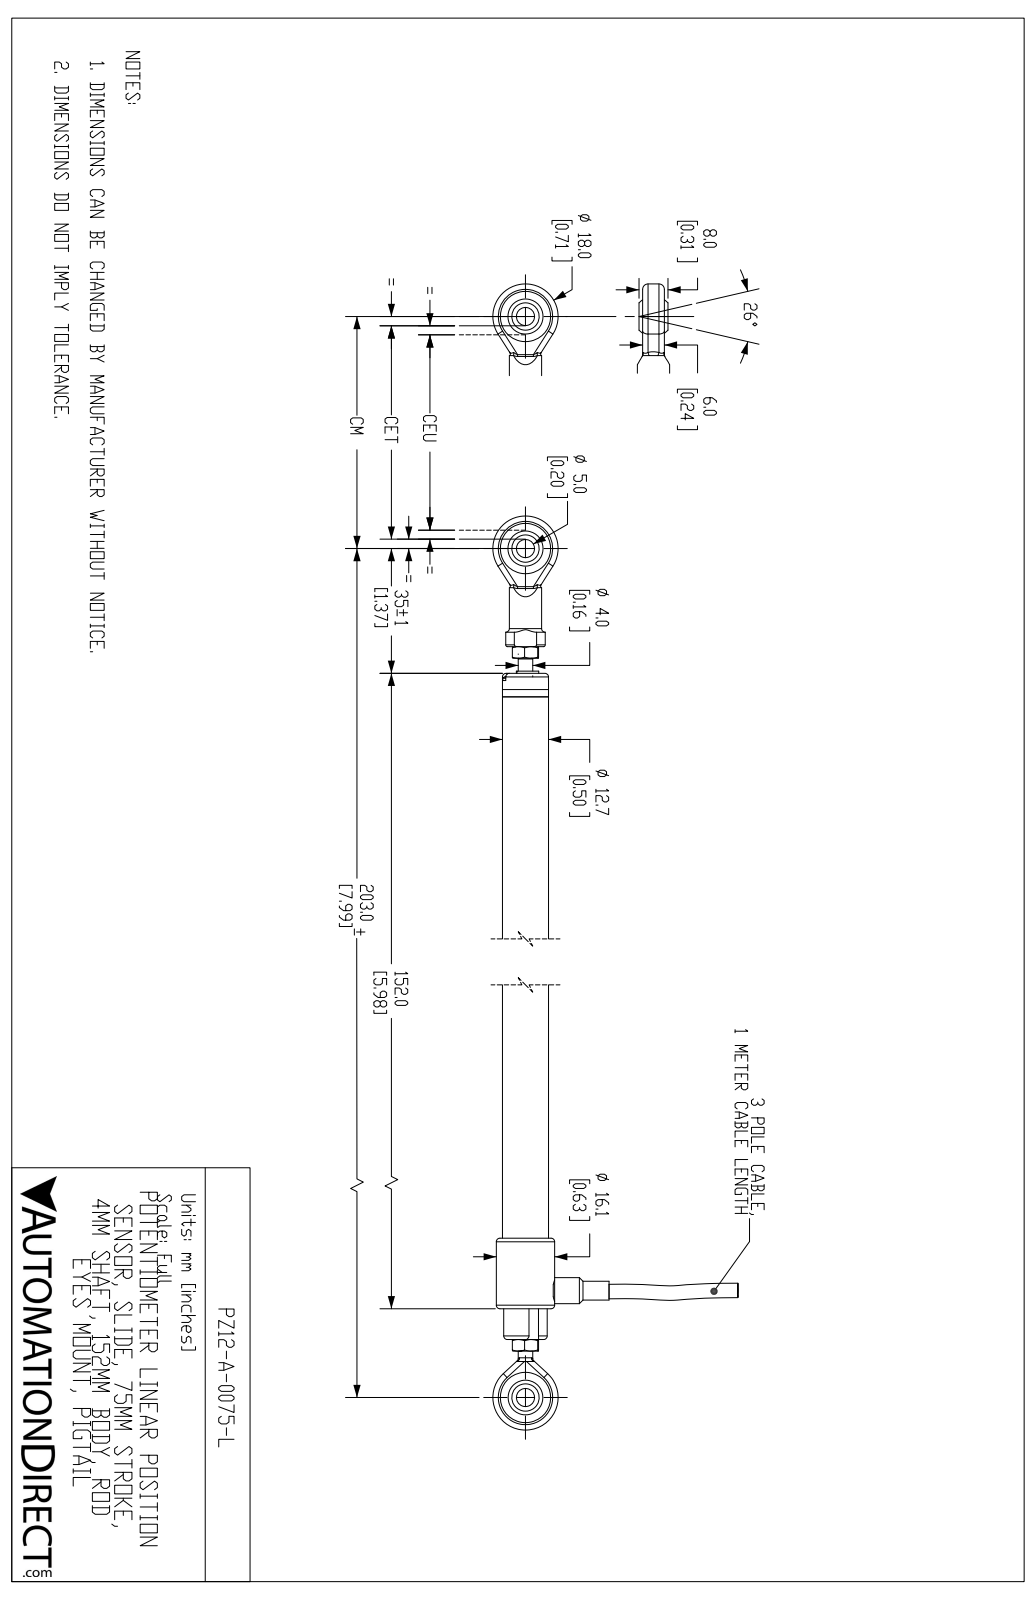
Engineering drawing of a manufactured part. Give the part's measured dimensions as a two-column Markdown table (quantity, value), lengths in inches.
| quantity | value |
| --- | --- |
| part name | PZ12-A-0075-L |
| STEP written by | SolidWorks 2019 (AUTOMOTIVE_DESIGN) |
| units | inches |
| bodies | 18 solids, 648 faces (168 planar, 170 cylindrical, 310 other) |
| overall size | 8.679 × 2.671 × 0.634 |
| volume | 1.724 in³ |
| surface area | 25.77 in² |
| round holes (diameter × count) | 0.138 × 3, 0.039 × 2, 0.055 × 2, 0.079 × 2, 0.197 × 2, 0.547 × 2, 0.126 × 1, 0.13 × 1, 0.201 × 1, 0.508 × 1 |
| round bosses / shafts (diameter × count) | 0.126 × 4, 0.063 × 4, 0.634 × 1, 0.5 × 1, 0.472 × 1, 0.35 × 1, 0.283 × 1, 0.236 × 1 |
| partial cylindrical surfaces (radius × count) | 0.059 × 8, 0.01 × 4, 0.02 × 2, 0.039 × 2, 0.069 × 2, 0.354 × 2, 0.017 × 1, 0.103 × 1 |
| main face-to-face distances | 0.079, 5.02, 5.098, 0.276, 0.224, 0.213, 0.236, 0.177, 6.274, 0.039 |
| hole center spacings | 0.189, 0.096, 0.167, 0.189, 0.248, 0.285, 0.339, 0.365 |
